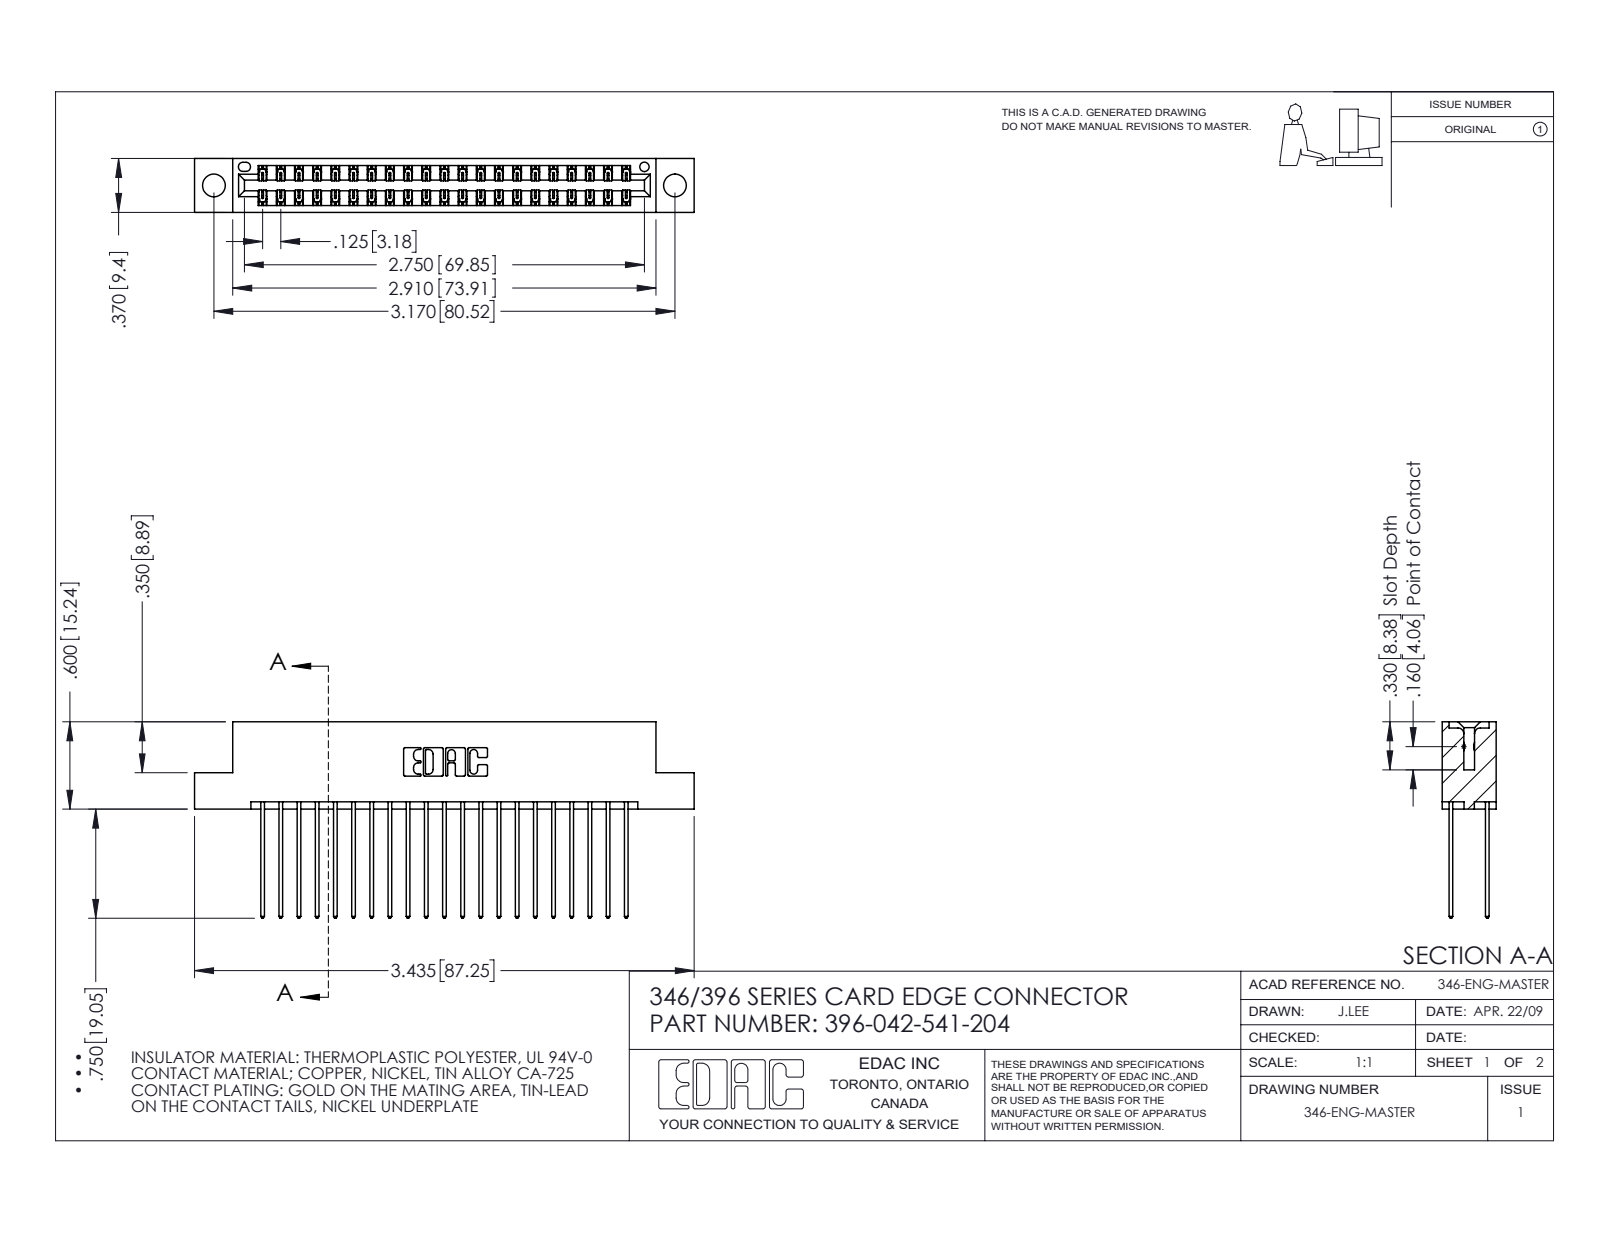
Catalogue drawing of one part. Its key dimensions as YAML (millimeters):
part_name: "396-042-541-204; 345-292-001_345-293-141; 346 Part_Flush Mounting Lugs - 0.156 Dia-TH"
step_written_by: "SolidWorks 2016 (CONFIG_CONTROL_DESIGN)"
units: millimeters
bodies: {solids: 43, faces: 2306, planar: 1546, cylindrical: 760, other: 0}
overall_size: [87.2, 34.3, 9.4]
volume: 8500
surface_area: 12320
round_holes:
  - {diameter: 4, count: 2}
  - {diameter: 1.6, count: 1}
partial_cylinders:
  - {radius: 0.2, count: 63}
  - {radius: 0.3, count: 42}
  - {radius: 0.3, count: 22}
  - {radius: 0.2, count: 6}
  - {radius: 0.8, count: 6}
  - {radius: 0.7, count: 3}
  - {radius: 0.4, count: 2}
  - {radius: 0.6, count: 2}
face_to_face_distances: [1.2, 8.2, 6.4, 1.8, 7.6, 0.6, 9.4, 7, 3.8, 5.6]
hole_center_spacings: [6.2, 75.3, 80.5]
